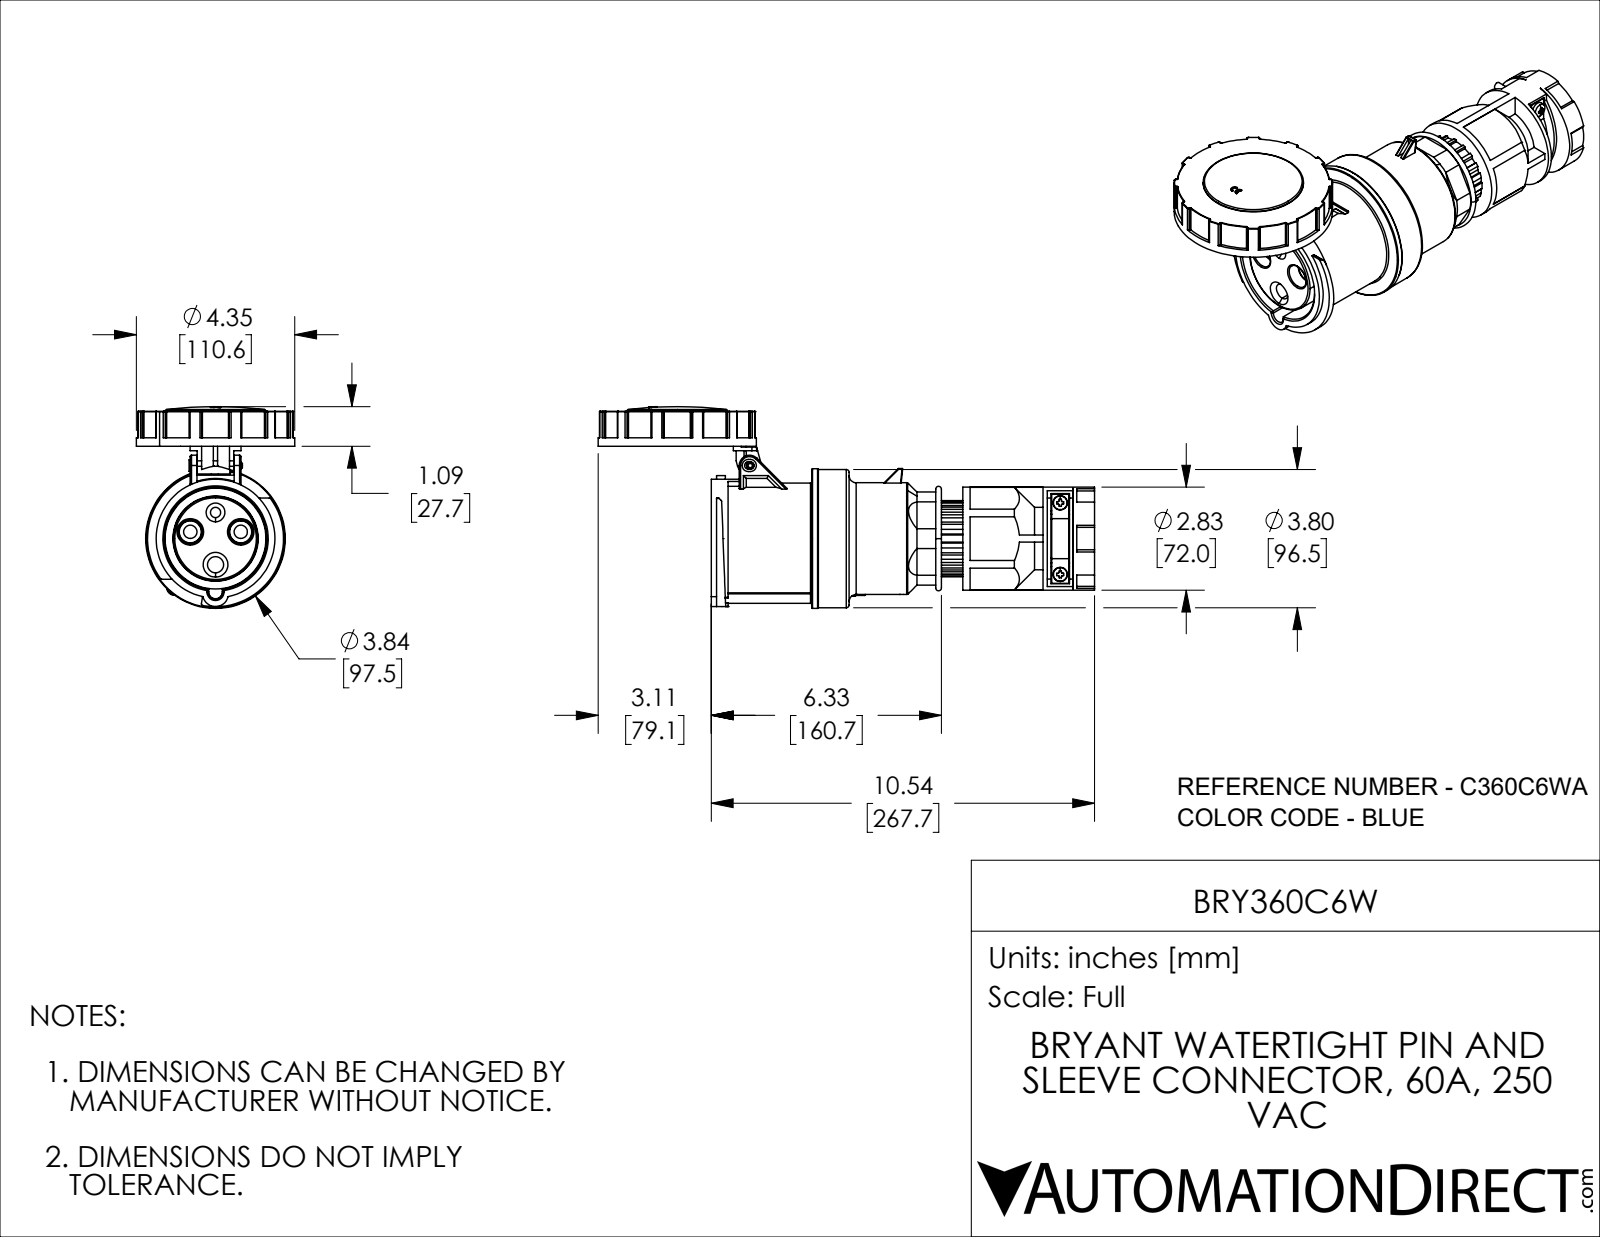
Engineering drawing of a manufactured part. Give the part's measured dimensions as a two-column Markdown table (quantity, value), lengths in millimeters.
| quantity | value |
| --- | --- |
| part name | BRY360C6W |
| STEP written by | SolidWorks 2021 (CONFIG_CONTROL_DESIGN) |
| units | millimeters |
| bodies | 2 solids, 1141 faces (474 planar, 391 cylindrical, 276 other) |
| overall size | 346.77 × 140.9 × 110.55 |
| volume | 1 155 000 mm³ |
| surface area | 180 755 mm² |
| round holes (diameter × count) | 9.3 × 2, 7.1 × 1, 11.3 × 1, 37 × 1, 65.5 × 1, 100.6 × 1 |
| round bosses / shafts (diameter × count) | 5 × 3, 110.55 × 1, 97.5 × 1, 96.5 × 1, 83 × 1, 78 × 1, 77.6 × 1, 72 × 1 |
| partial cylindrical surfaces (radius × count) | 0.3 × 48, 1 × 40, 0.5 × 15, 34.5 × 6, 0.4 × 4, 2 × 4, 1.75 × 2, 2.5 × 2 |
| main face-to-face distances | 21.5, 3, 65, 26, 15.5, 92, 15, 161.5, 5, 90.5 |
| hole center spacings | 18.25, 22.22, 28.96, 35.26, 36.5 |
